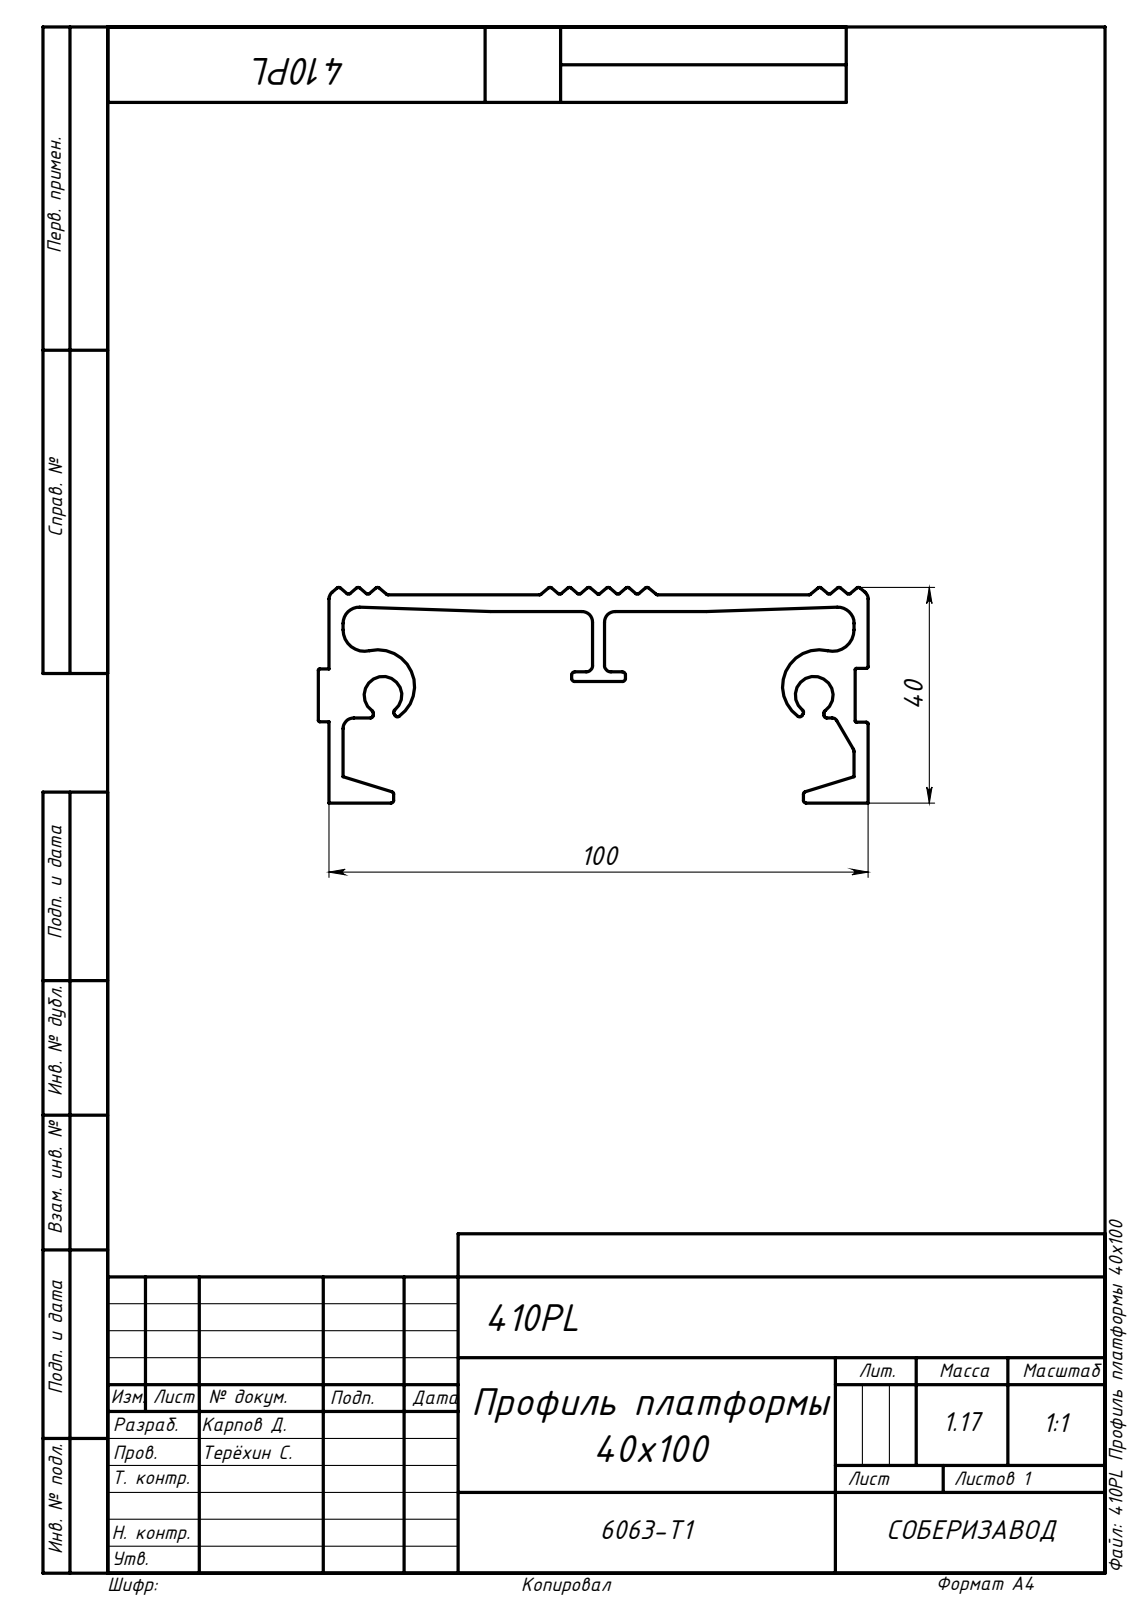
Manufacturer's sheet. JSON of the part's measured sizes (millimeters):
{"part_name": "410PL Профиль платформы 40х100", "step_written_by": "SolidWorks 2016 (AUTOMOTIVE_DESIGN)", "units": "millimeters", "bodies": {"solids": 1, "faces": 136, "planar": 66, "cylindrical": 70, "other": 0}, "overall_size": [1000, 102, 40.03], "volume_mm3": 846662, "surface_area_mm2": 505837, "round_holes": [[7, 2]], "partial_cylinders_radius": [[0.4, 24], [0.5, 12], [0.25, 4], [0.6, 4], [0.3, 3], [2, 3], [1, 2], [1.2, 2]], "face_to_face_distances": [3.1, 100, 35.55, 38.65, 32, 25.09, 48.9, 51.1, 2.3, 4.61], "hole_center_spacings": [80]}
